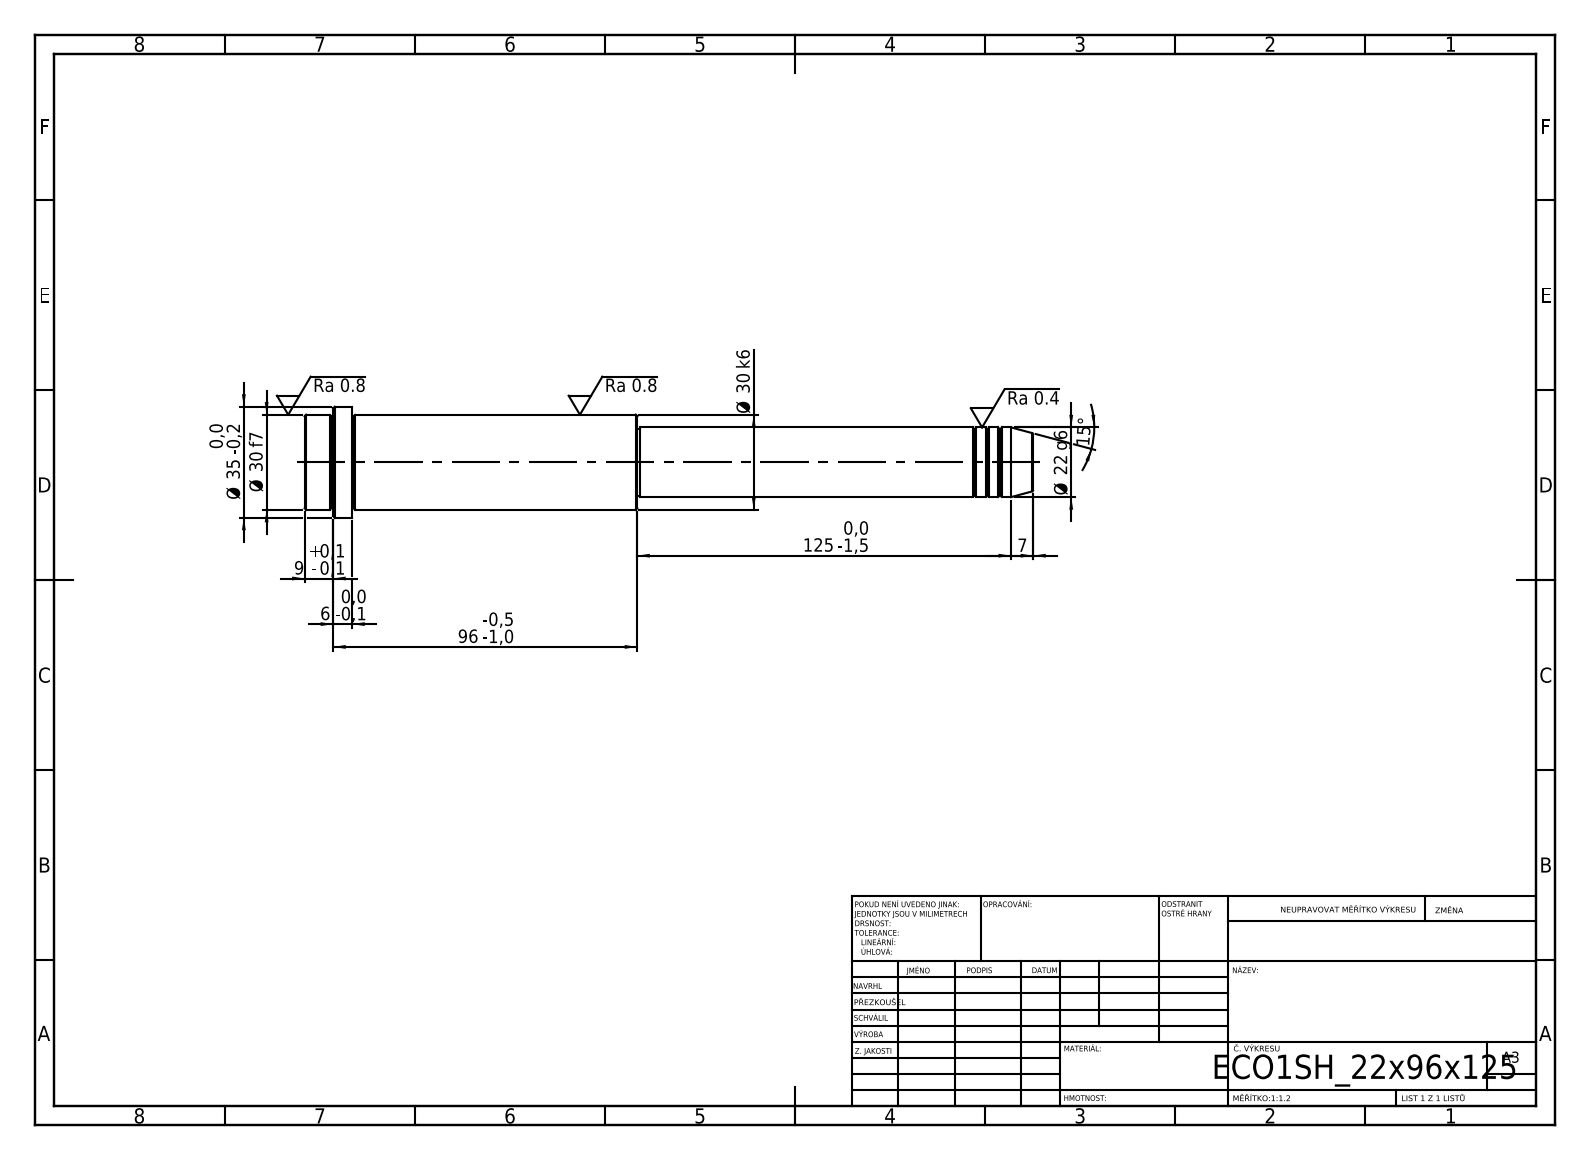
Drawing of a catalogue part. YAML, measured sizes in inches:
step_written_by: "SolidWorks 2019 (CONFIG_CONTROL_DESIGN)"
units: inches
bodies: {solids: 1, faces: 52, planar: 6, cylindrical: 16, other: 30}
overall_size: [9.055, 1.378, 1.378]
volume: 7.482
surface_area: 31.91
round_bosses_or_shafts:
  - {diameter: 1.378, count: 1}
  - {diameter: 1.181, count: 1}
  - {diameter: 0.866, count: 1}
  - {diameter: 0.827, count: 1}
face_to_face_distances: [4.134, 3.543, 0.591, 4.921, 8.465, 9.055, 8.701, 3.78, 0.236, 0.354]
